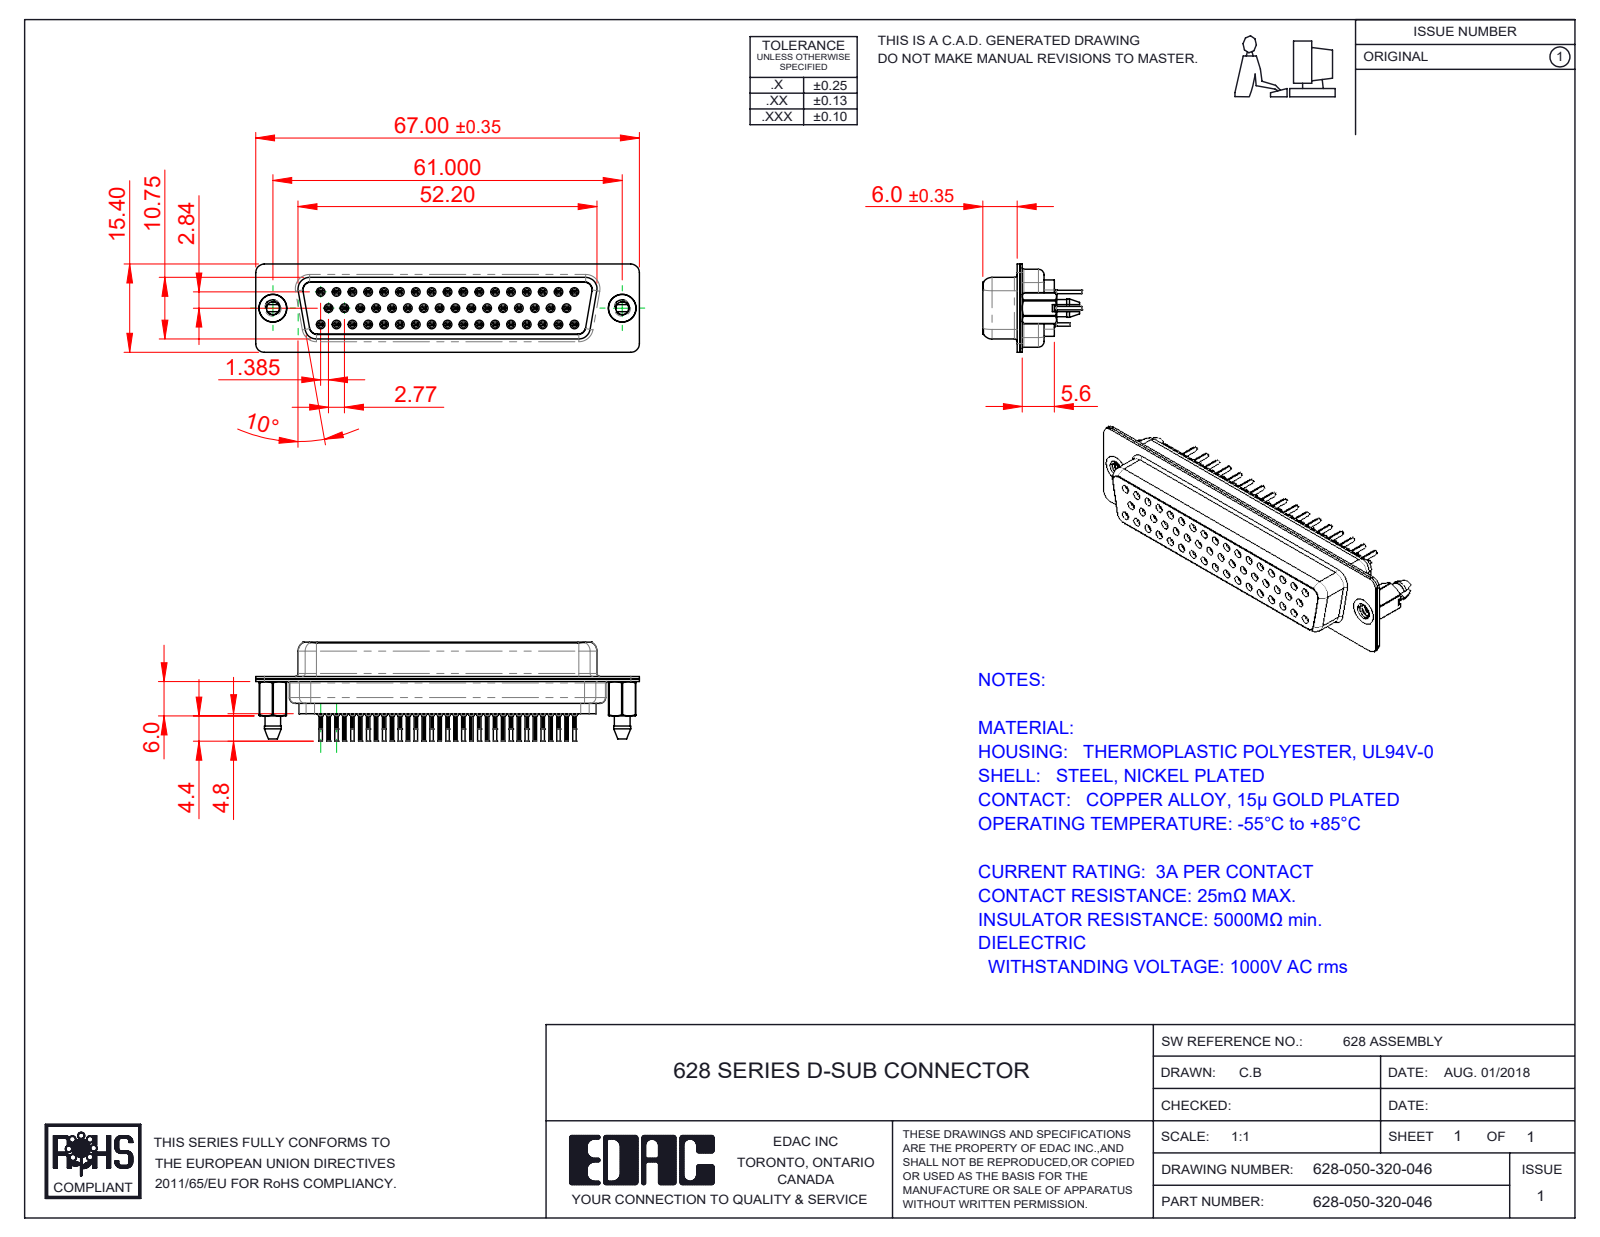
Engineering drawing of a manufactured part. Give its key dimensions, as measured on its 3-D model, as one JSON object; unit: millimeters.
{"part_name": "628-050-320-046; 628 4-40 Threaded Boardlock_LP; 628 Shell Front_50 Contacts; 628 Contact Row 3_20L (+4 more)", "step_written_by": "SolidWorks 2020 (CONFIG_CONTROL_DESIGN)", "units": "millimeters", "bodies": {"solids": 55, "faces": 6703, "planar": 1649, "cylindrical": 1819, "other": 3235}, "overall_size": [67, 17.3, 15.4], "volume_mm3": 6837, "surface_area_mm2": 15567, "round_holes": [[0.2, 50], [0.8, 50], [0.9, 50], [1.1, 50], [1.6, 50], [1.7, 17], [2.26, 2], [4, 2], [4.05, 2], [4.85, 2]], "round_bosses_or_shafts": [[2, 50], [1.5, 50], [1.2, 50], [0.6, 50], [4.95, 2], [4.8, 2]], "partial_cylinders_radius": [[0.1, 100], [0.28, 33], [1.5, 18], [2, 12], [1.35, 8], [1.6, 6], [0.25, 4], [0.5, 4]], "face_to_face_distances": [0.45, 0.4, 11.33, 1.87, 10.3, 6.5, 0.9, 6.05, 6, 6.45], "hole_center_spacings": [3.16, 2.77, 5.54, 8.31, 11.08, 13.85, 16.62, 19.39]}
